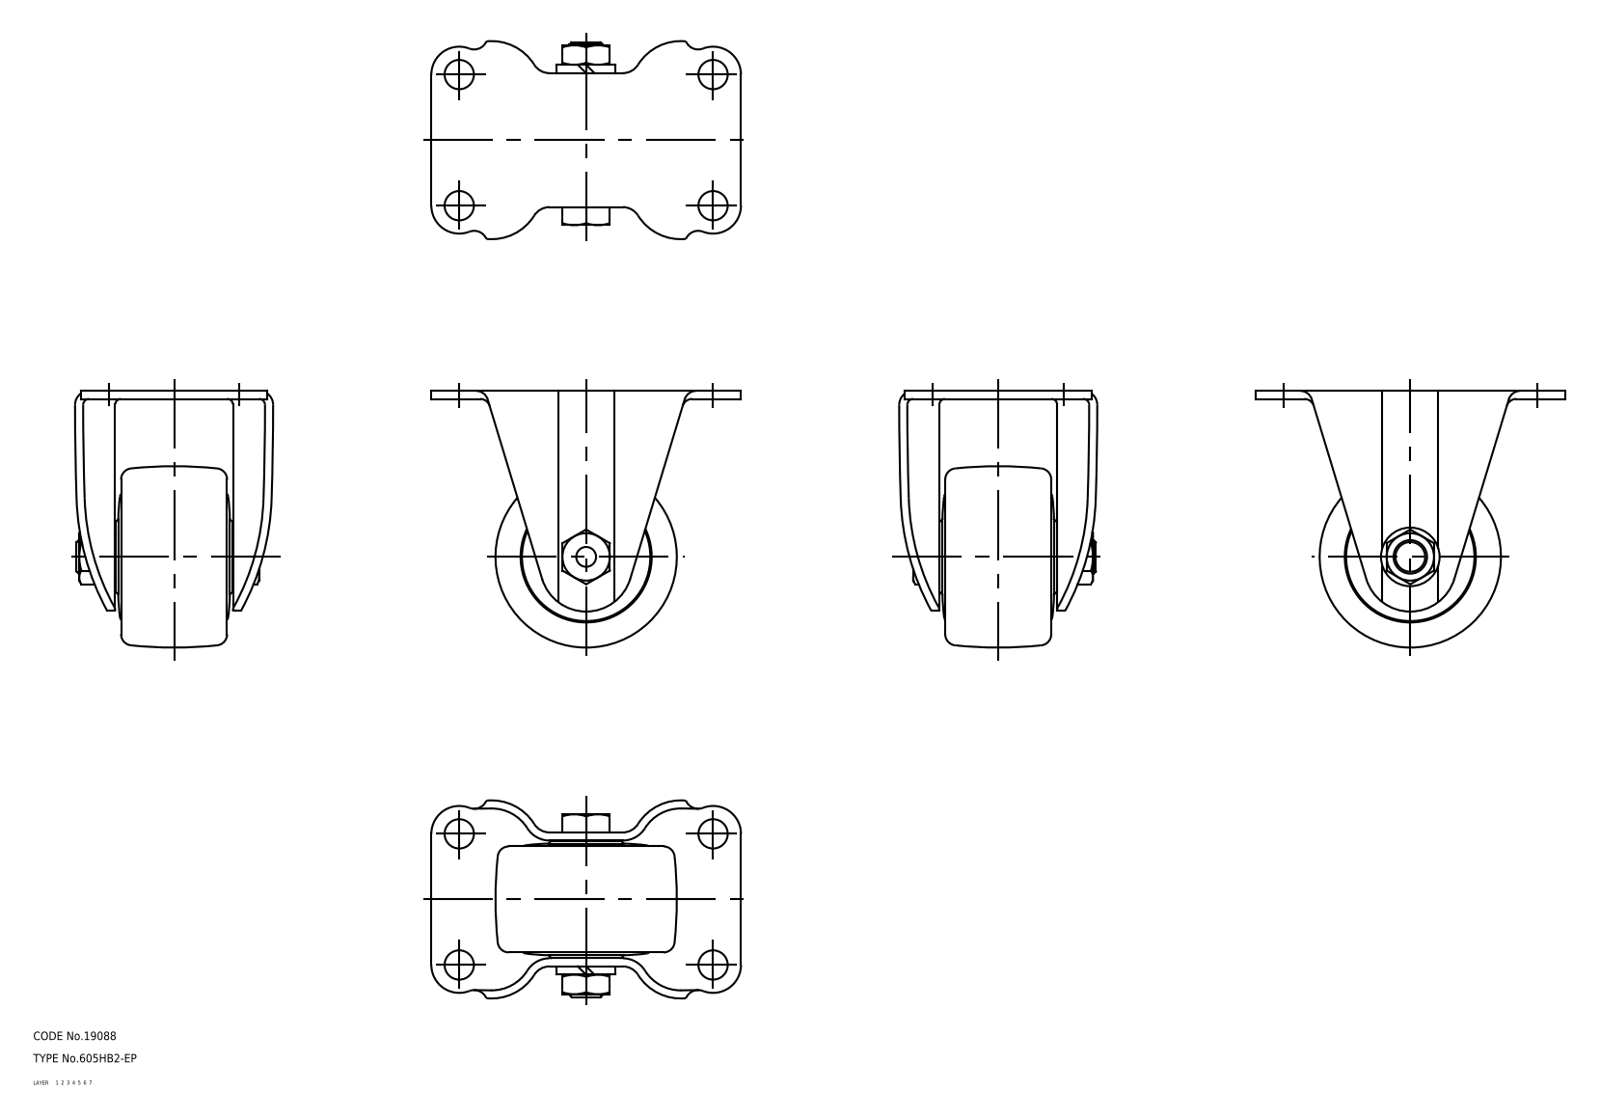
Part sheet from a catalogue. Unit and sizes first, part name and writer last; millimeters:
Units: millimetres
Overall size (bounding box): 111 × 92 × 71
Volume: 170 217 mm³ · Surface area: 50 114 mm²
Bodies: 3 solids, 172 faces (0 planar, 0 cylindrical, 172 other)
Part name (STEP PRODUCT): wheel; axle; No_605HB2_EP_15701_36
STEP written by: CADfix (AUTOMOTIVE_DESIGN)
